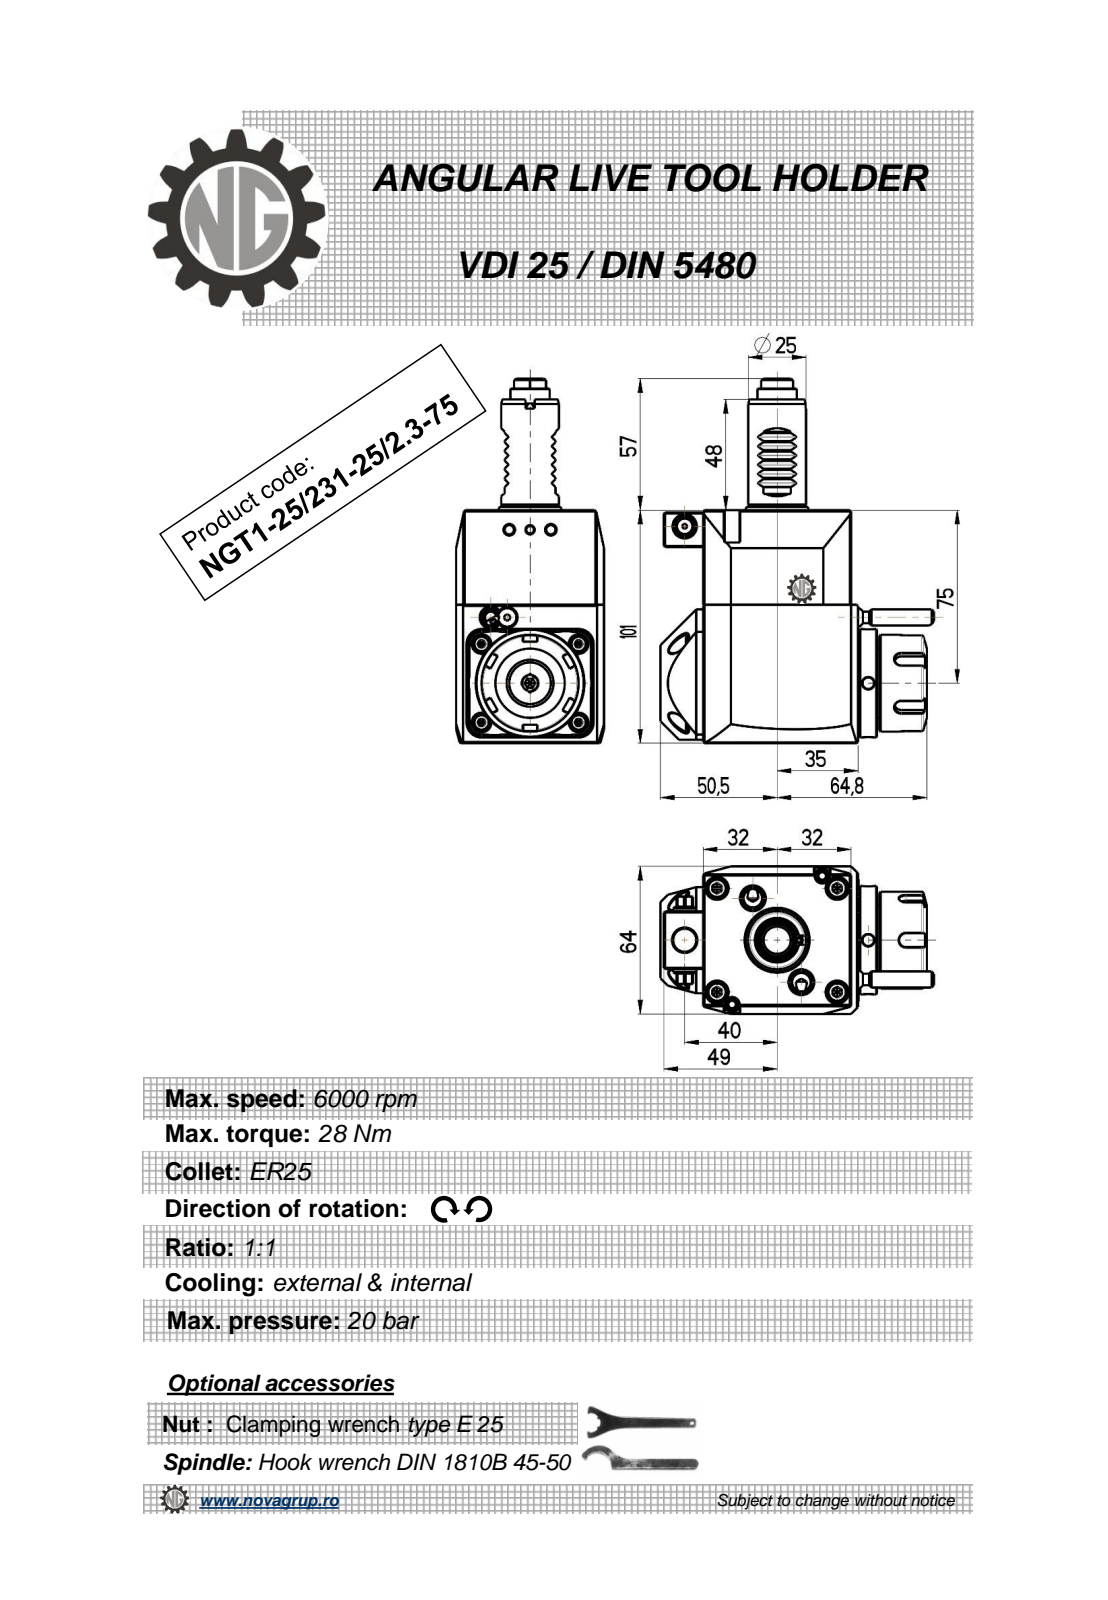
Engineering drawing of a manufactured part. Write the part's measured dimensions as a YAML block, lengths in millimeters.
part_name: "NGT1_25_231_25_2_3_75"
step_written_by: "PRO/ENGINEER BY PARAMETRIC TECHNOLOGY CORPORATION, 2010280 (CONFIG_CONTROL_DESIGN)"
units: millimeters
bodies: {solids: 1, faces: 521, planar: 199, cylindrical: 157, other: 165}
overall_size: [158, 118.33, 64]
volume: 518937
surface_area: 49925
round_holes:
  - {diameter: 5, count: 2}
  - {diameter: 8.5, count: 2}
  - {diameter: 2, count: 1}
  - {diameter: 2.5, count: 1}
  - {diameter: 3, count: 1}
  - {diameter: 10, count: 1}
  - {diameter: 20.3, count: 1}
round_bosses_or_shafts:
  - {diameter: 7.96, count: 2}
  - {diameter: 47, count: 1}
  - {diameter: 42, count: 1}
  - {diameter: 36.4, count: 1}
  - {diameter: 33, count: 1}
  - {diameter: 25, count: 1}
  - {diameter: 17, count: 1}
  - {diameter: 10, count: 1}
partial_cylinders:
  - {radius: 1.9, count: 32}
  - {radius: 0.3, count: 12}
  - {radius: 3, count: 5}
  - {radius: 3.85, count: 1}
  - {radius: 6.08, count: 1}
  - {radius: 6.92, count: 1}
  - {radius: 10.5, count: 1}
  - {radius: 32, count: 1}
face_to_face_distances: [64, 101, 3.2, 67.2, 8, 3, 67, 18.5, 82.5, 85.5]
hole_center_spacings: [33.19, 41.63, 66.5, 79.45, 104.58]
